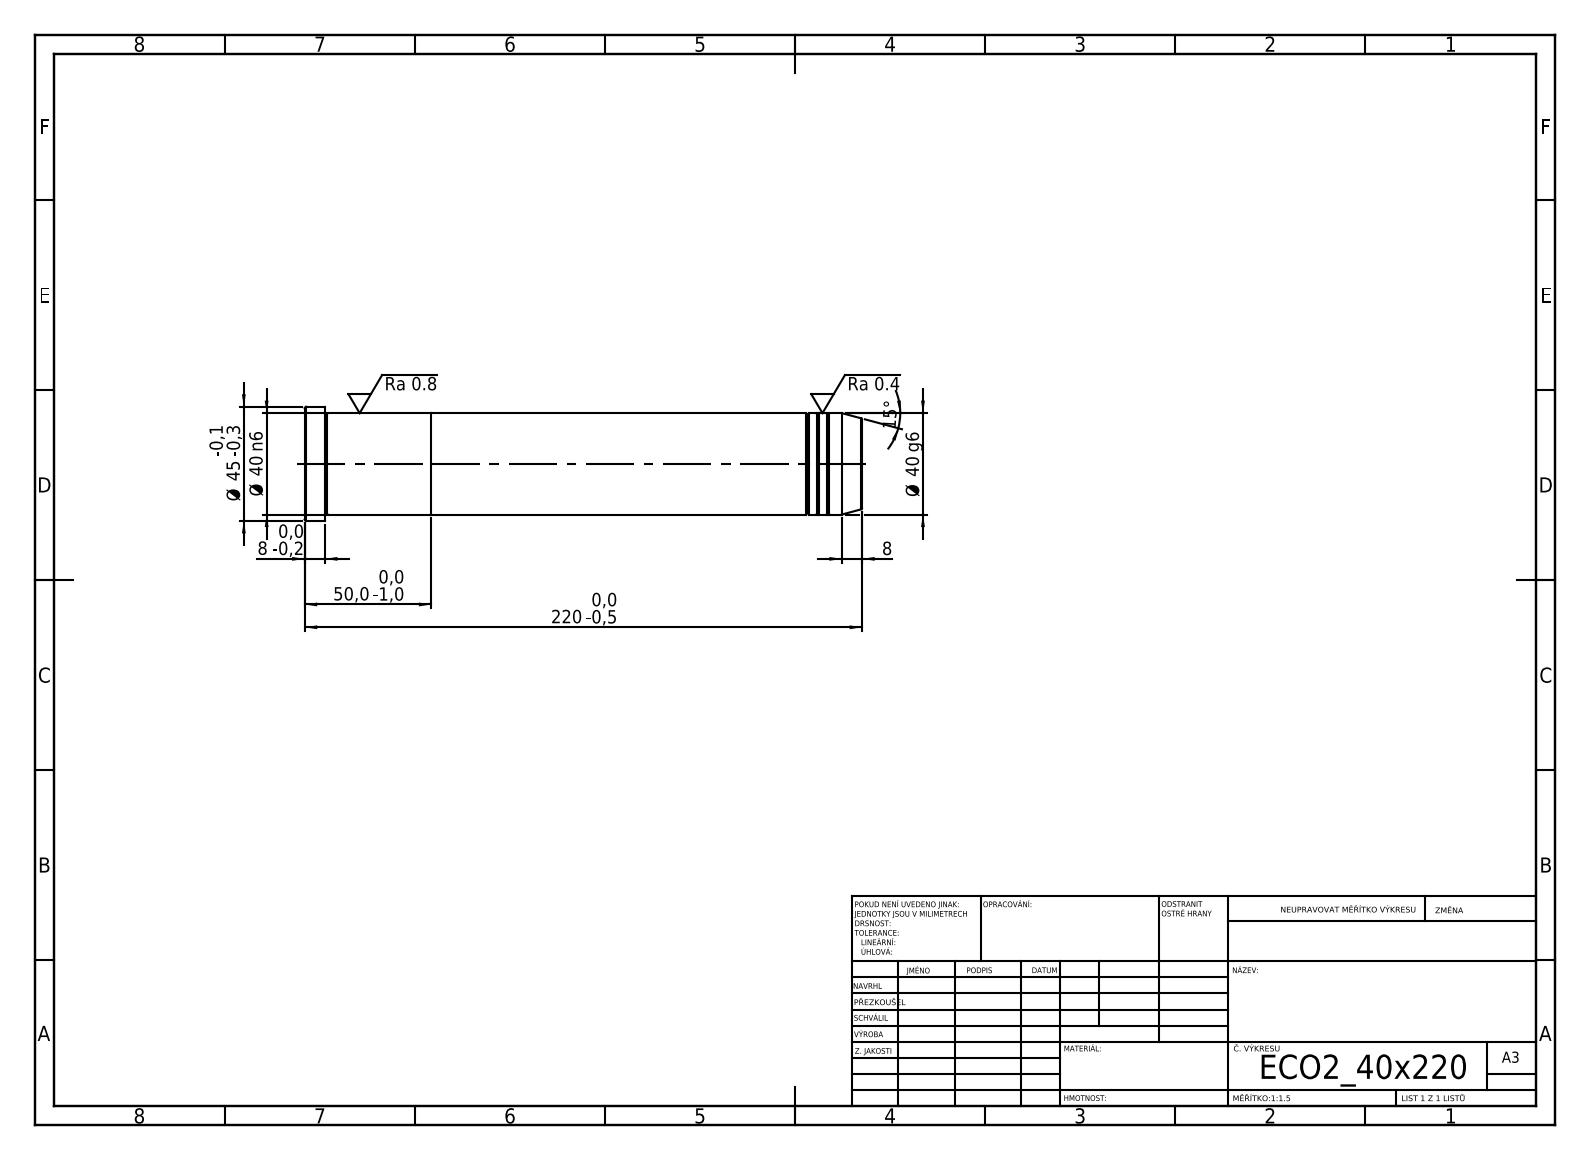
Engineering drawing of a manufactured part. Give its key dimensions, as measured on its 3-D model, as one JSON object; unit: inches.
{"step_written_by": "SolidWorks 2019 (CONFIG_CONTROL_DESIGN)", "units": "inches", "bodies": {"solids": 2, "faces": 39, "planar": 5, "cylindrical": 12, "other": 22}, "overall_size": [8.661, 1.772, 1.772], "volume_in3": 16.96, "surface_area_in2": 51.79, "round_bosses_or_shafts": [[1.772, 1], [1.575, 1]], "face_to_face_distances": [1.969, 6.693, 8.661, 8.346, 1.654, 0.315]}
